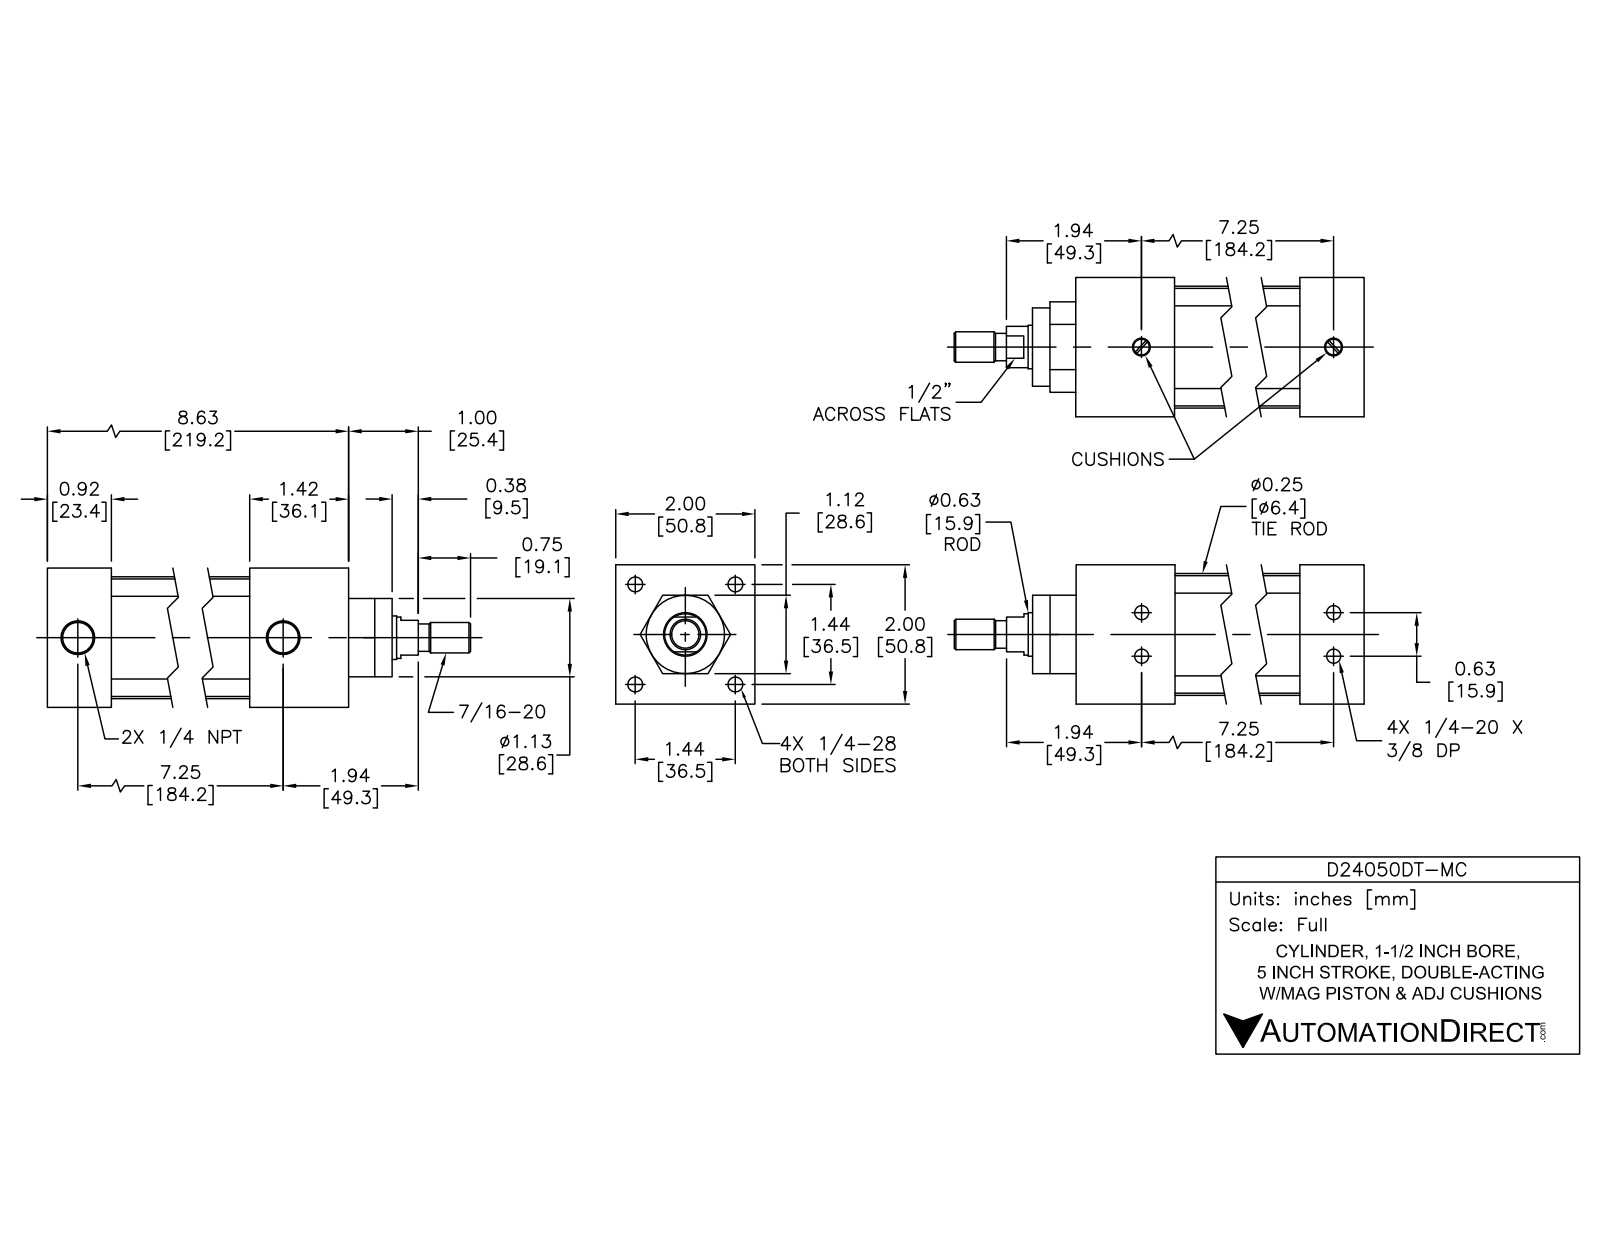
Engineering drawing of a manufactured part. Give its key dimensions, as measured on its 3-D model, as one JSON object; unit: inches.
{"part_name": "D24050DT-MC; D24050DT-M PISTON; D24050DT-M BODY", "step_written_by": "SolidWorks 2015 (AUTOMOTIVE_DESIGN)", "units": "inches", "bodies": {"solids": 12, "faces": 303, "planar": 99, "cylindrical": 114, "other": 90}, "overall_size": [10.371, 2, 2], "volume_in3": 18.17, "surface_area_in2": 167.8, "round_holes": [[0.196, 4], [0.211, 4], [0.281, 4], [0.406, 4], [0.297, 2], [0.477, 2], [0.625, 1], [0.628, 1], [1.5, 1]], "round_bosses_or_shafts": [[0.39, 4], [0.25, 4], [0.222, 4], [1.75, 1], [1.497, 1], [1.121, 1], [0.622, 1], [0.59, 1]], "partial_cylinders_radius": [[0.2, 4]], "face_to_face_distances": [2, 8.621, 1.42, 7.201, 7.701, 6.281, 0.92, 1.121, 7.601, 6.181], "hole_center_spacings": [0.313, 1.014, 1.434, 0.625, 2.028, 7.247, 7.252, 7.253]}
